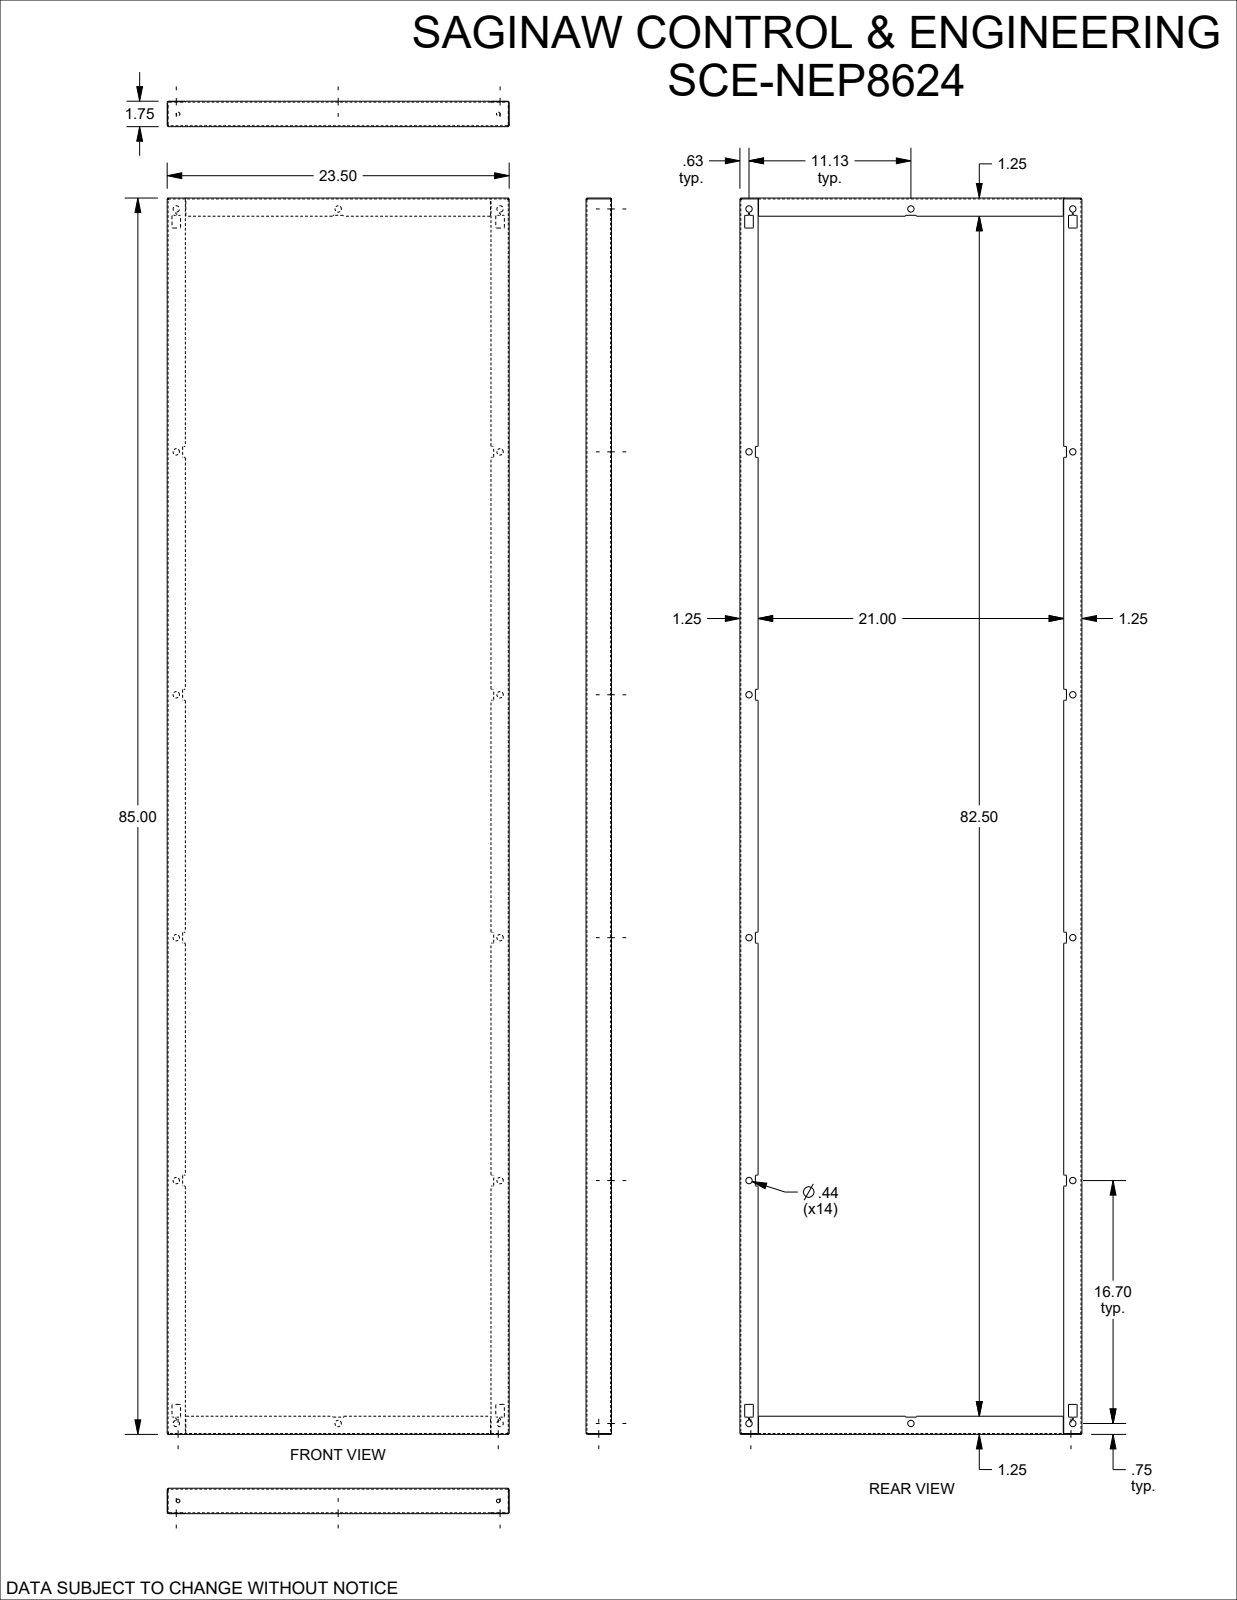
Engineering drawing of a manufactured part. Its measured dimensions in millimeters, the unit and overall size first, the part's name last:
Units: millimetres
Overall size (bounding box): 2159 × 596.9 × 44.5
Round holes (diameter × count): ⌀11.1 ×14
Partial cylindrical surfaces — rounded edges, fillets, slot ends (radius × count): R0.8 ×72
Main face-to-face distances: 1.5, 42.9, 595.4, 44.5, 41.4, 596.9, 593.9, 2157.5, 2159, 2156
Hole centre spacings: 424.2, 706.6, 848.4, 1019.4, 565.2, 1272.5, 1392.4, 894.2
Volume: 2 560 000 mm³ · Surface area: 3 377 000 mm²
Bodies: 1 solid, 174 faces (88 planar, 86 cylindrical, 0 other)
Part name (STEP PRODUCT): SCE-NEP8624SS6
STEP written by: SolidWorks 2023 (AUTOMOTIVE_DESIGN)
